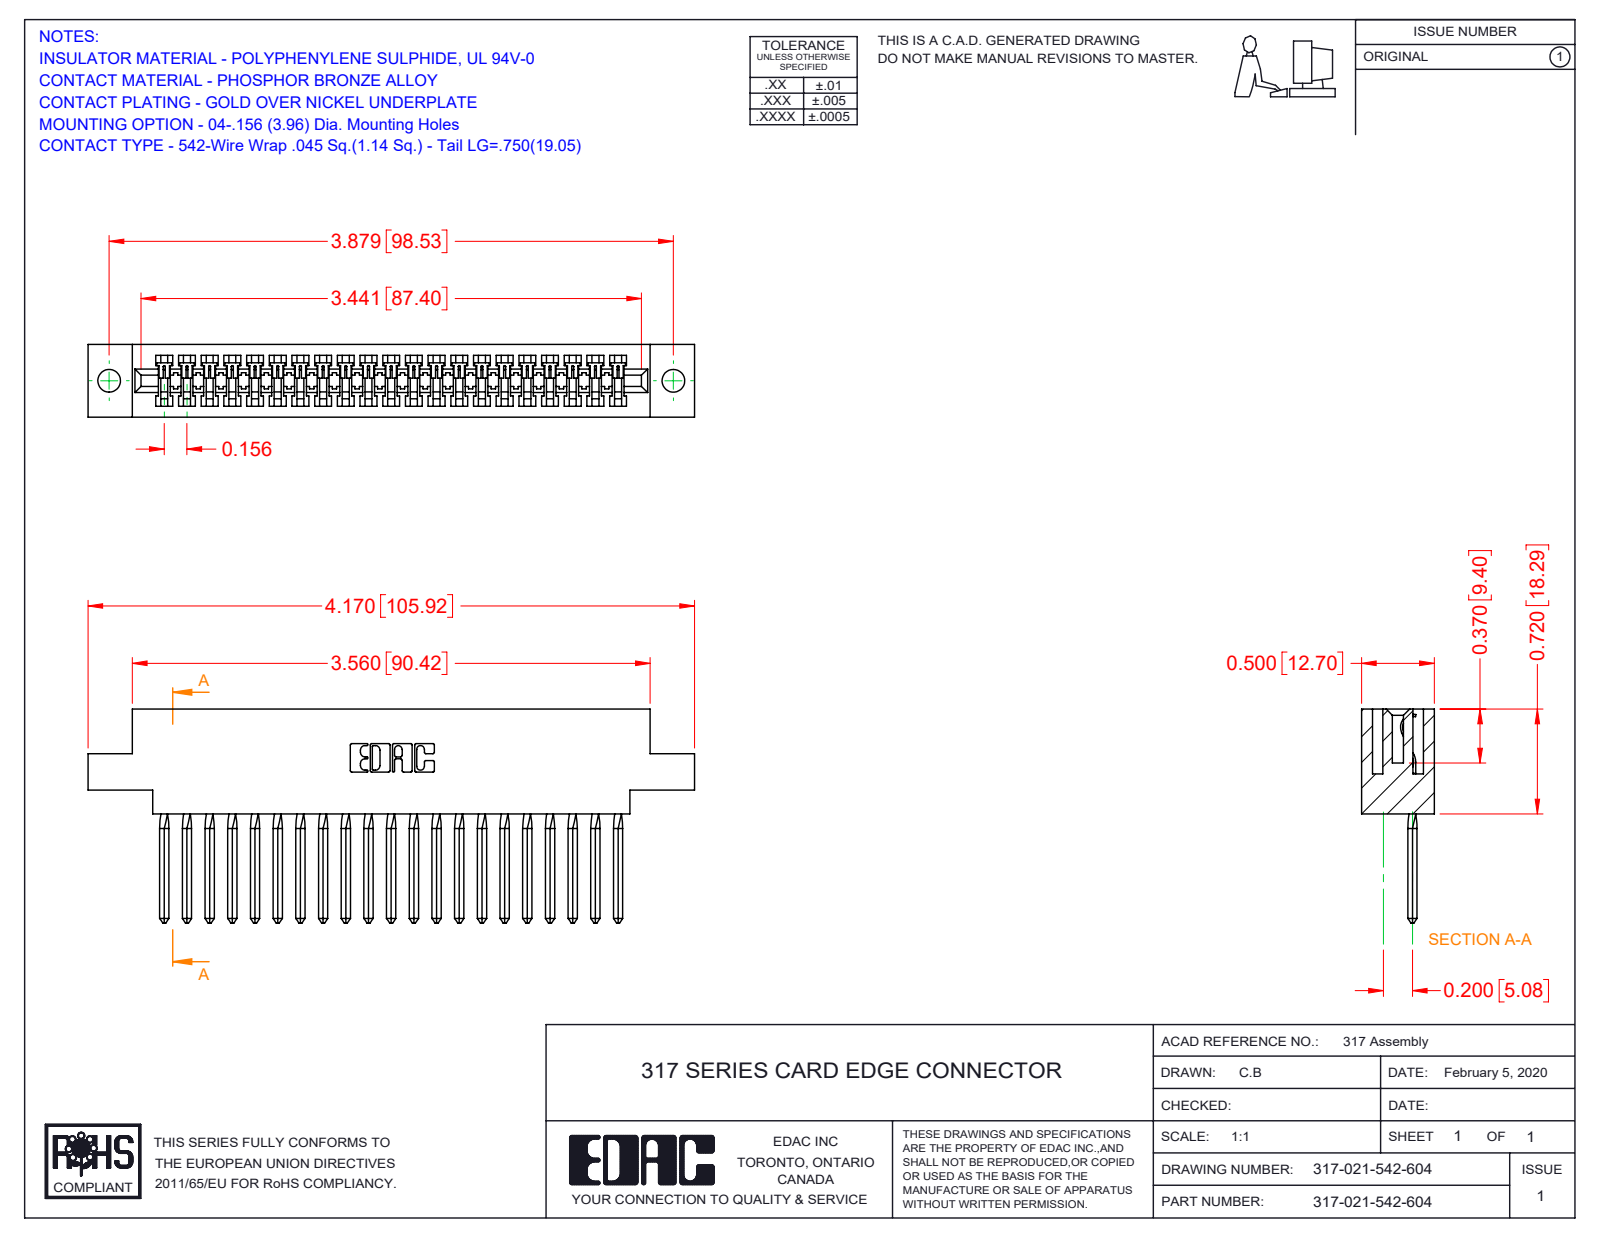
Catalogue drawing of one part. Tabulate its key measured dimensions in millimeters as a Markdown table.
| quantity | value |
| --- | --- |
| part name | 317-021-542-604; 317 Part_.156 Dia - TH; 317-290-003_542 |
| STEP written by | SolidWorks 2016 (CONFIG_CONTROL_DESIGN) |
| units | millimeters |
| bodies | 22 solids, 1677 faces (1402 planar, 191 cylindrical, 84 other) |
| overall size | 105.9 × 37.3 × 12.7 |
| volume | 15 700 mm³ |
| surface area | 18 500 mm² |
| round holes (diameter × count) | 4 × 2 |
| partial cylindrical surfaces (radius × count) | 0.2 × 42, 0.3 × 22, 0.2 × 6, 0.8 × 6, 0.7 × 3, 1.9 × 1, 2.3 × 1, 2.5 × 1 |
| main face-to-face distances | 12.7, 1.9, 10.8, 8.9, 2.8, 3.5, 18.3, 5.4, 7.3, 5.4 |
| hole center spacings | 98.5 |
